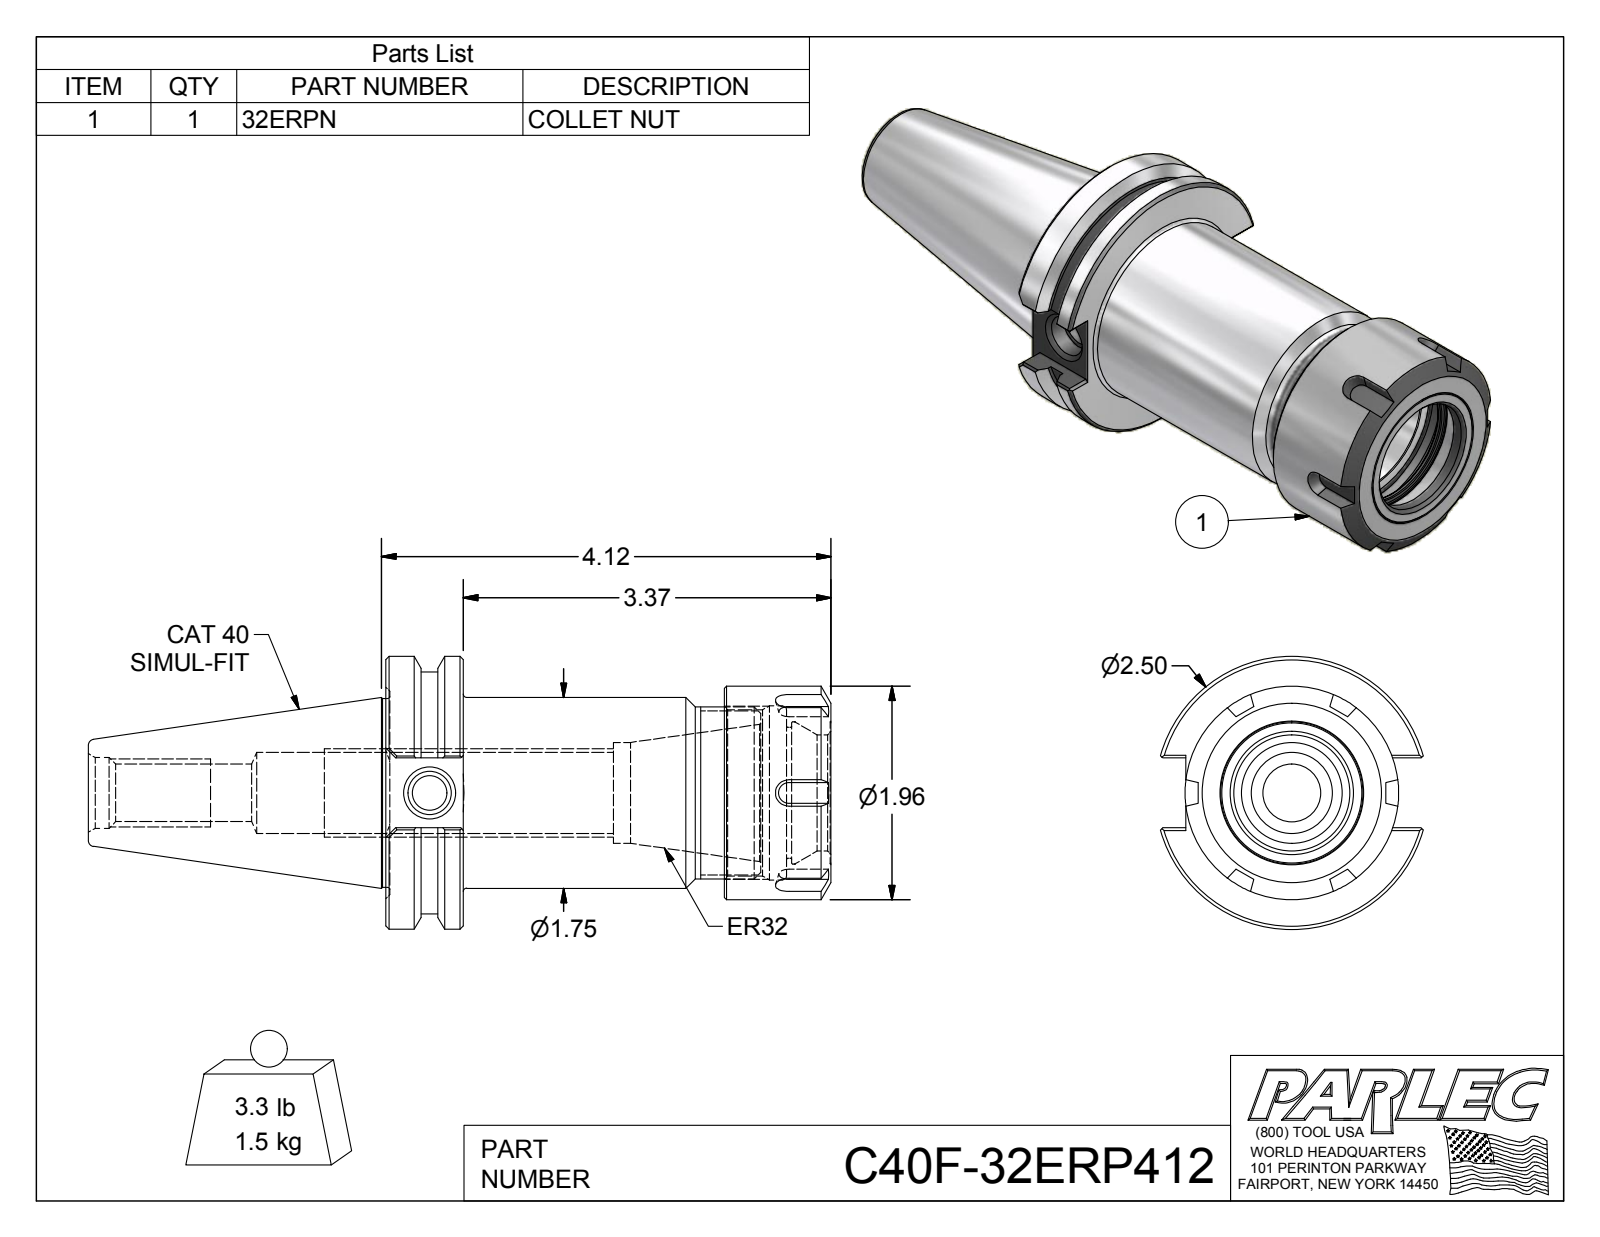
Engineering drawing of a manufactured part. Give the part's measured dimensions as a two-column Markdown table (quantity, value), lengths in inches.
| quantity | value |
| --- | --- |
| part name | C40F-32ERP412; C40F-32ER4-1; 32ERPN |
| STEP written by | Autodesk Inventor 2012 (AUTOMOTIVE_DESIGN) |
| units | inches |
| bodies | 2 solids, 123 faces (56 planar, 21 cylindrical, 46 other) |
| overall size | 6.808 × 2.5 × 2.406 |
| volume | 11.62 in³ |
| surface area | 68.96 in² |
| round holes (diameter × count) | 0.315 × 1, 0.399 × 1, 0.527 × 1, 0.648 × 1, 0.745 × 1, 0.925 × 1, 1.063 × 1, 1.2 × 1, 1.305 × 1, 1.523 × 1, 1.595 × 1 |
| round bosses / shafts (diameter × count) | 2.5 × 1, 2.215 × 1, 1.958 × 1, 1.75 × 1, 1.73 × 1, 1.575 × 1 |
| main face-to-face distances | 0.711, 4.081, 3.37, 3.103, 2.392, 0.978, 3.674, 2.963, 0.571, 0.407 |
